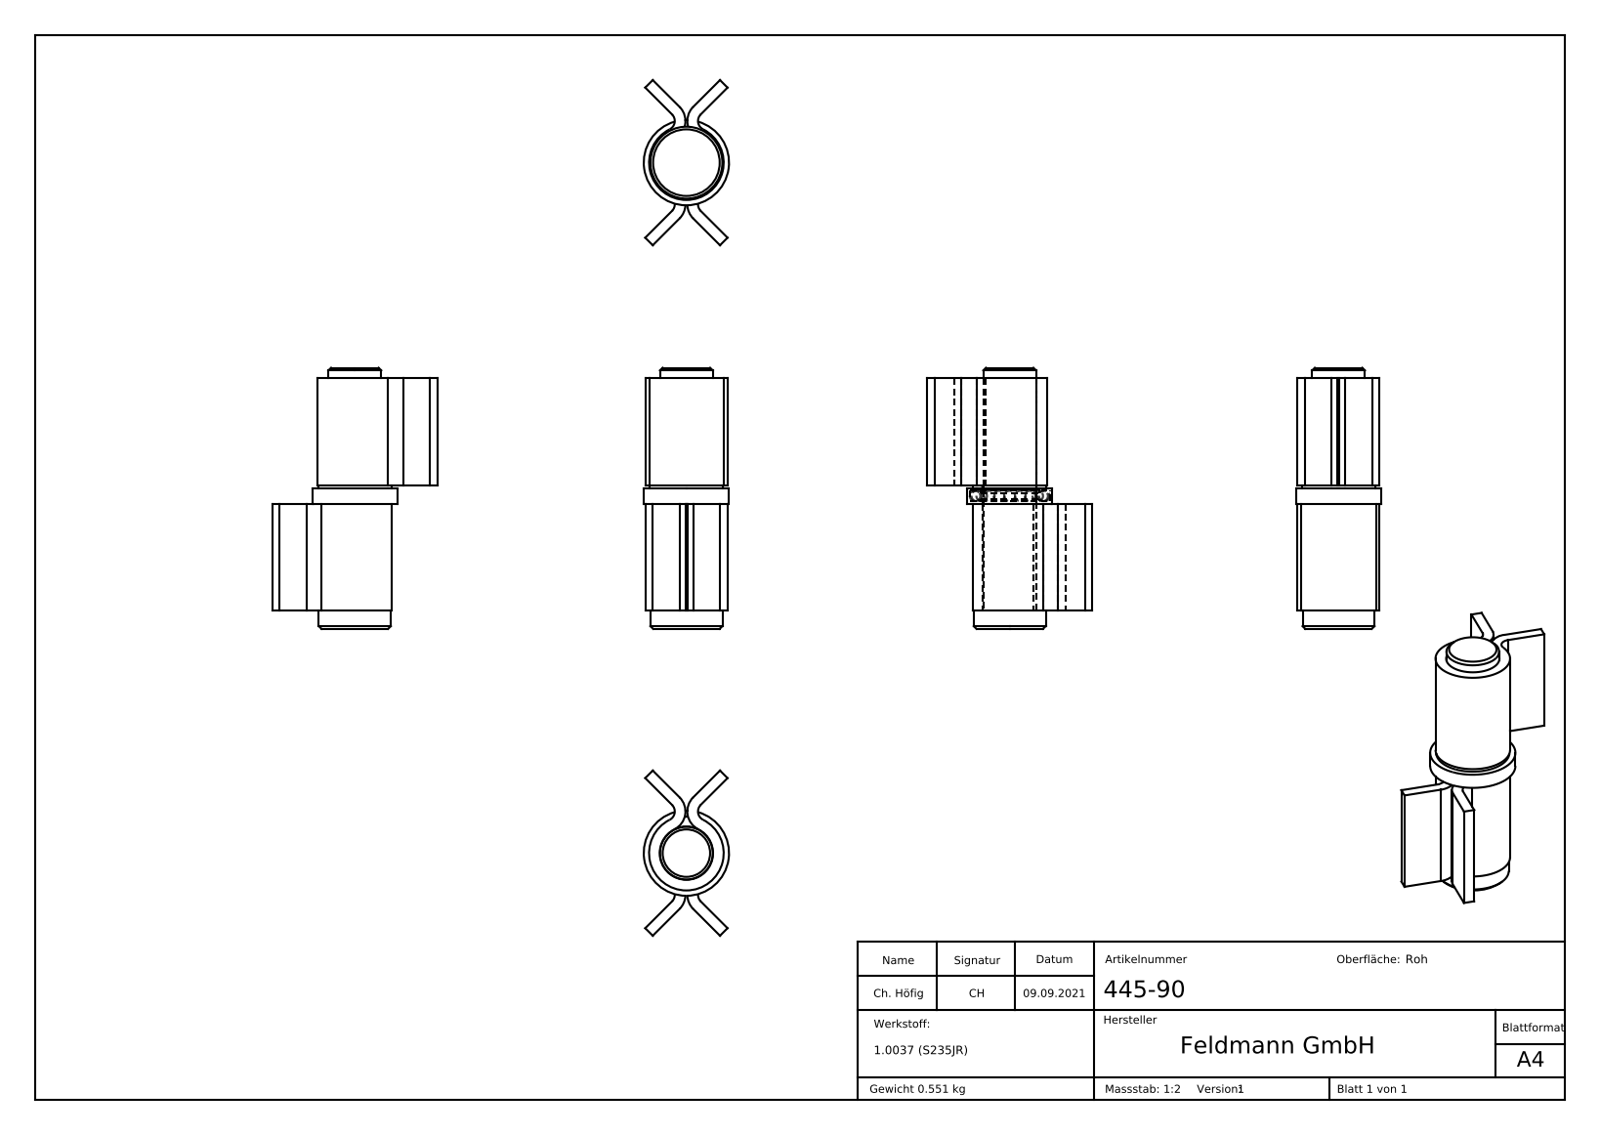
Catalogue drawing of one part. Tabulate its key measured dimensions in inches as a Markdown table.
| quantity | value |
| --- | --- |
| part name | 445-90 Teil2; 445-90 Teil3; 445-90 Teil2_445-90 Teil2; 445-90 Teil3_445-90 Teil3 (+3 more) |
| STEP written by | SolidWorks 2018 (CONFIG_CONTROL_DESIGN) |
| units | inches |
| bodies | 24 solids, 302 faces (142 planar, 44 cylindrical, 116 other) |
| overall size | 3.858 × 2.441 × 1.26 |
| volume | 4.312 in³ |
| surface area | 50.06 in² |
| round holes (diameter × count) | 0.787 × 1, 1.083 × 1, 1.181 × 1 |
| round bosses / shafts (diameter × count) | 1.26 × 1, 1.102 × 1, 1.079 × 1, 1.063 × 1, 0.866 × 1, 0.78 × 1 |
| partial cylindrical surfaces (radius × count) | 0.138 × 4, 0.295 × 4, 0.398 × 1 |
| main face-to-face distances | 0.157, 0.866, 1.85, 0.276, 1.575, 1.024, 0.709, 0.702, 0.86, 1.569 |
